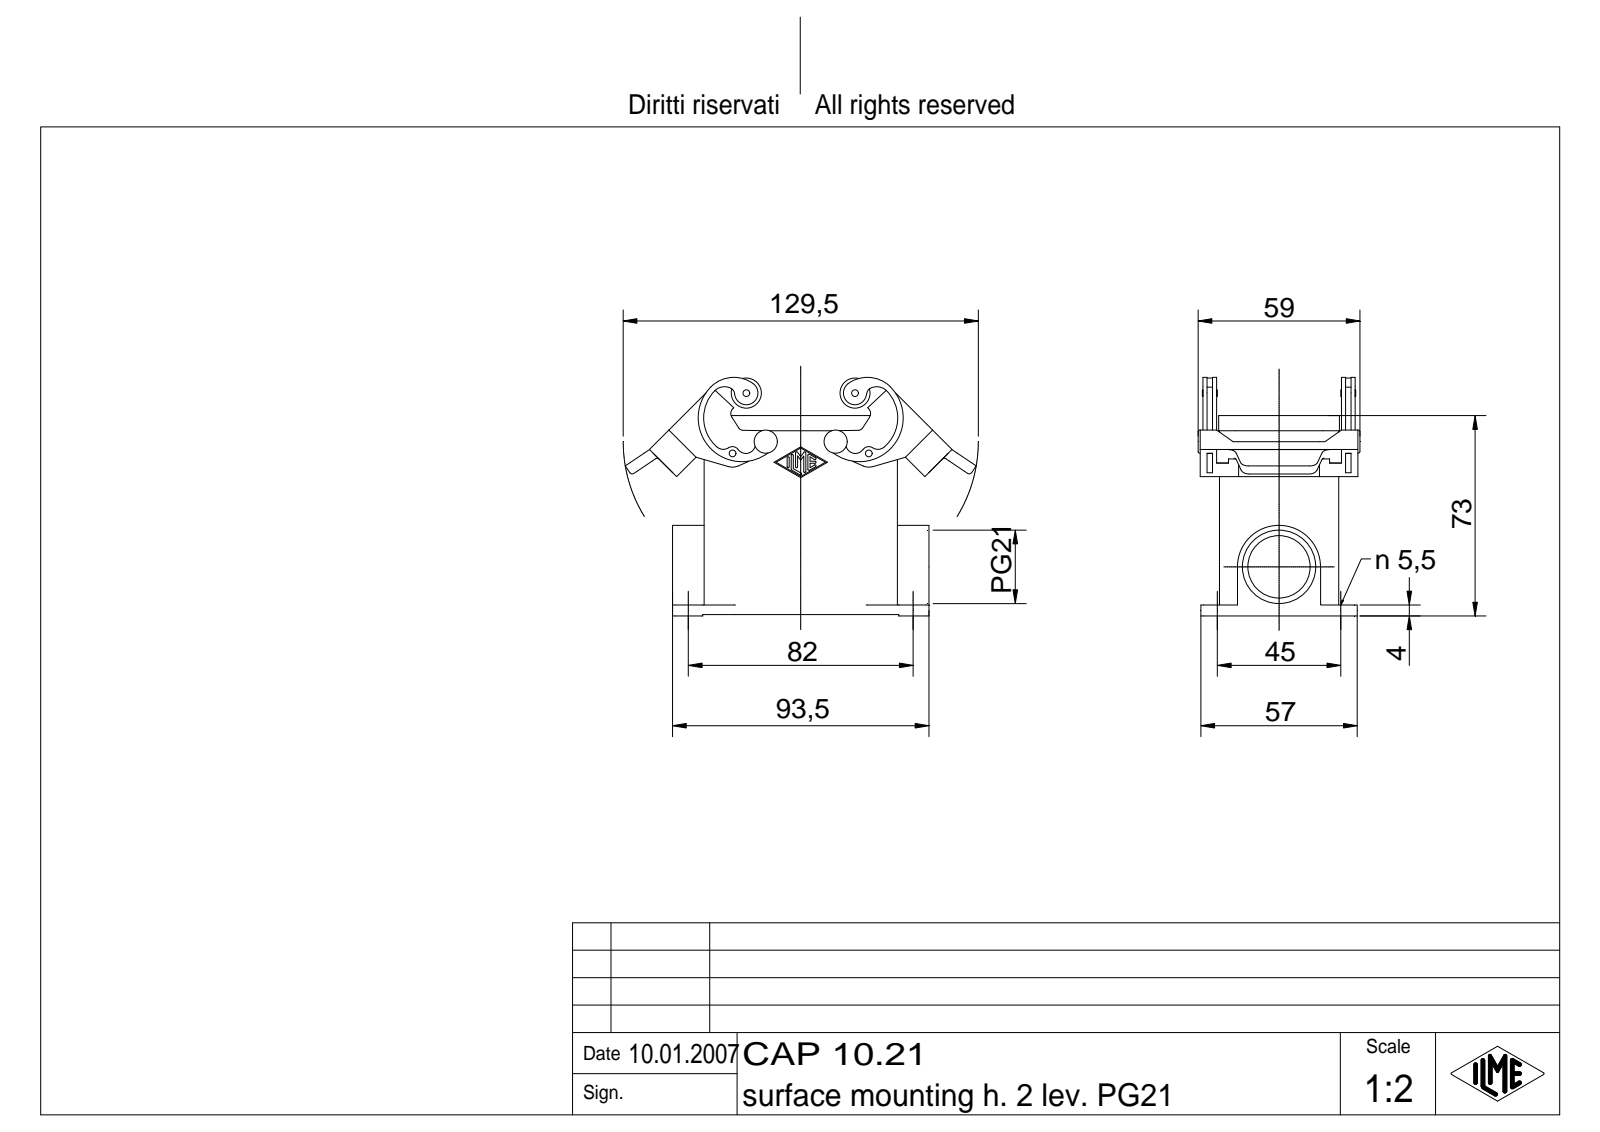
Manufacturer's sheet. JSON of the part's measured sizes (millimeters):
{"part_name": "CAP 10.21", "step_written_by": "Autodesk Inventor 7 (AUTOMOTIVE_DESIGN)", "units": "millimeters", "bodies": {"solids": 1, "faces": 749, "planar": 191, "cylindrical": 205, "other": 353}, "overall_size": [127.99, 86.94, 58], "volume_mm3": 106810, "surface_area_mm2": 58220, "round_holes": [[2, 4], [5.5, 4], [2.5, 2], [22.78, 1], [26.78, 1]], "round_bosses_or_shafts": [[11, 2], [5, 2], [3, 2]], "partial_cylinders_radius": [[1, 20], [0.38, 14], [3, 12], [6, 8], [2.5, 6], [1.5, 4], [2, 4], [3.5, 4]], "face_to_face_distances": [3, 40.5, 43.5, 37.5, 3.5, 4, 50.5, 0.75, 4.5, 2.5], "hole_center_spacings": [22.56, 45, 49.78, 82, 93.54, 39.64, 49.68]}
